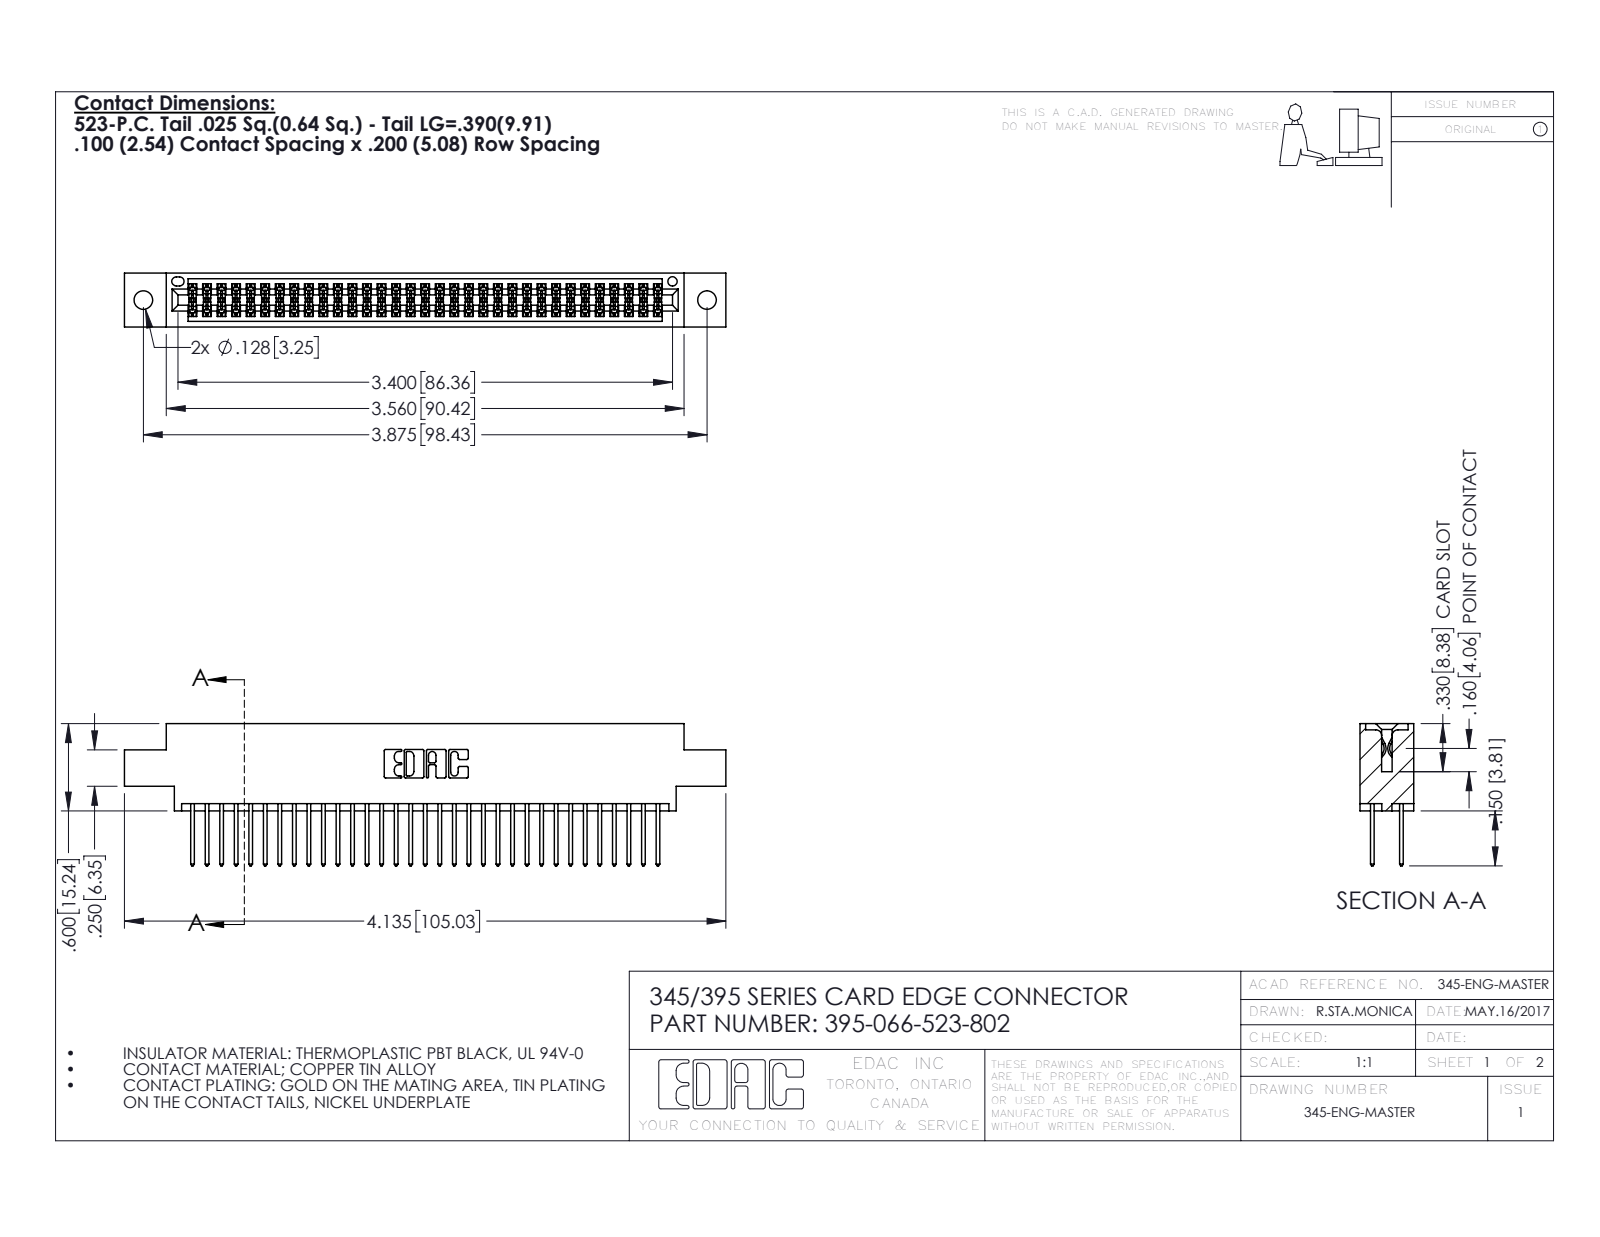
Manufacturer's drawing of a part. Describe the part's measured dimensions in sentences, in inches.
The part is named "345-292-001_345-293-123; 395-066-523-802; 345 Part_0.170 Offset - 0.128 Dia". Its 3-D file was written by "SolidWorks 2016 (CONFIG_CONTROL_DESIGN)". It is 67 solids with 3430 faces: 2262 planar, 1168 cylindrical and 0 other. Overall it measures 4.135 by 0.977 by 0.37 inches. Its volume is 0.617 cubic inches and its surface area 23.62 square inches. Round holes: 2 of diameter 0.128, 1 of diameter 0.064. Partial cylindrical surfaces (rounded edges, fillets, slot ends): 99 of radius 0.006, 66 of radius 0.01, 22 of radius 0.01, 6 of radius 0.007, 6 of radius 0.031, 3 of radius 0.026, 2 of radius 0.014, 2 of radius 0.019. The main face-to-face distances are 0.298, 0.072, 0.2, 0.098, 0.272, 0.025, 0.37, 0.225, 0.175, 0.149. The hole center spacings are 0.27, 3.64, 3.875.
